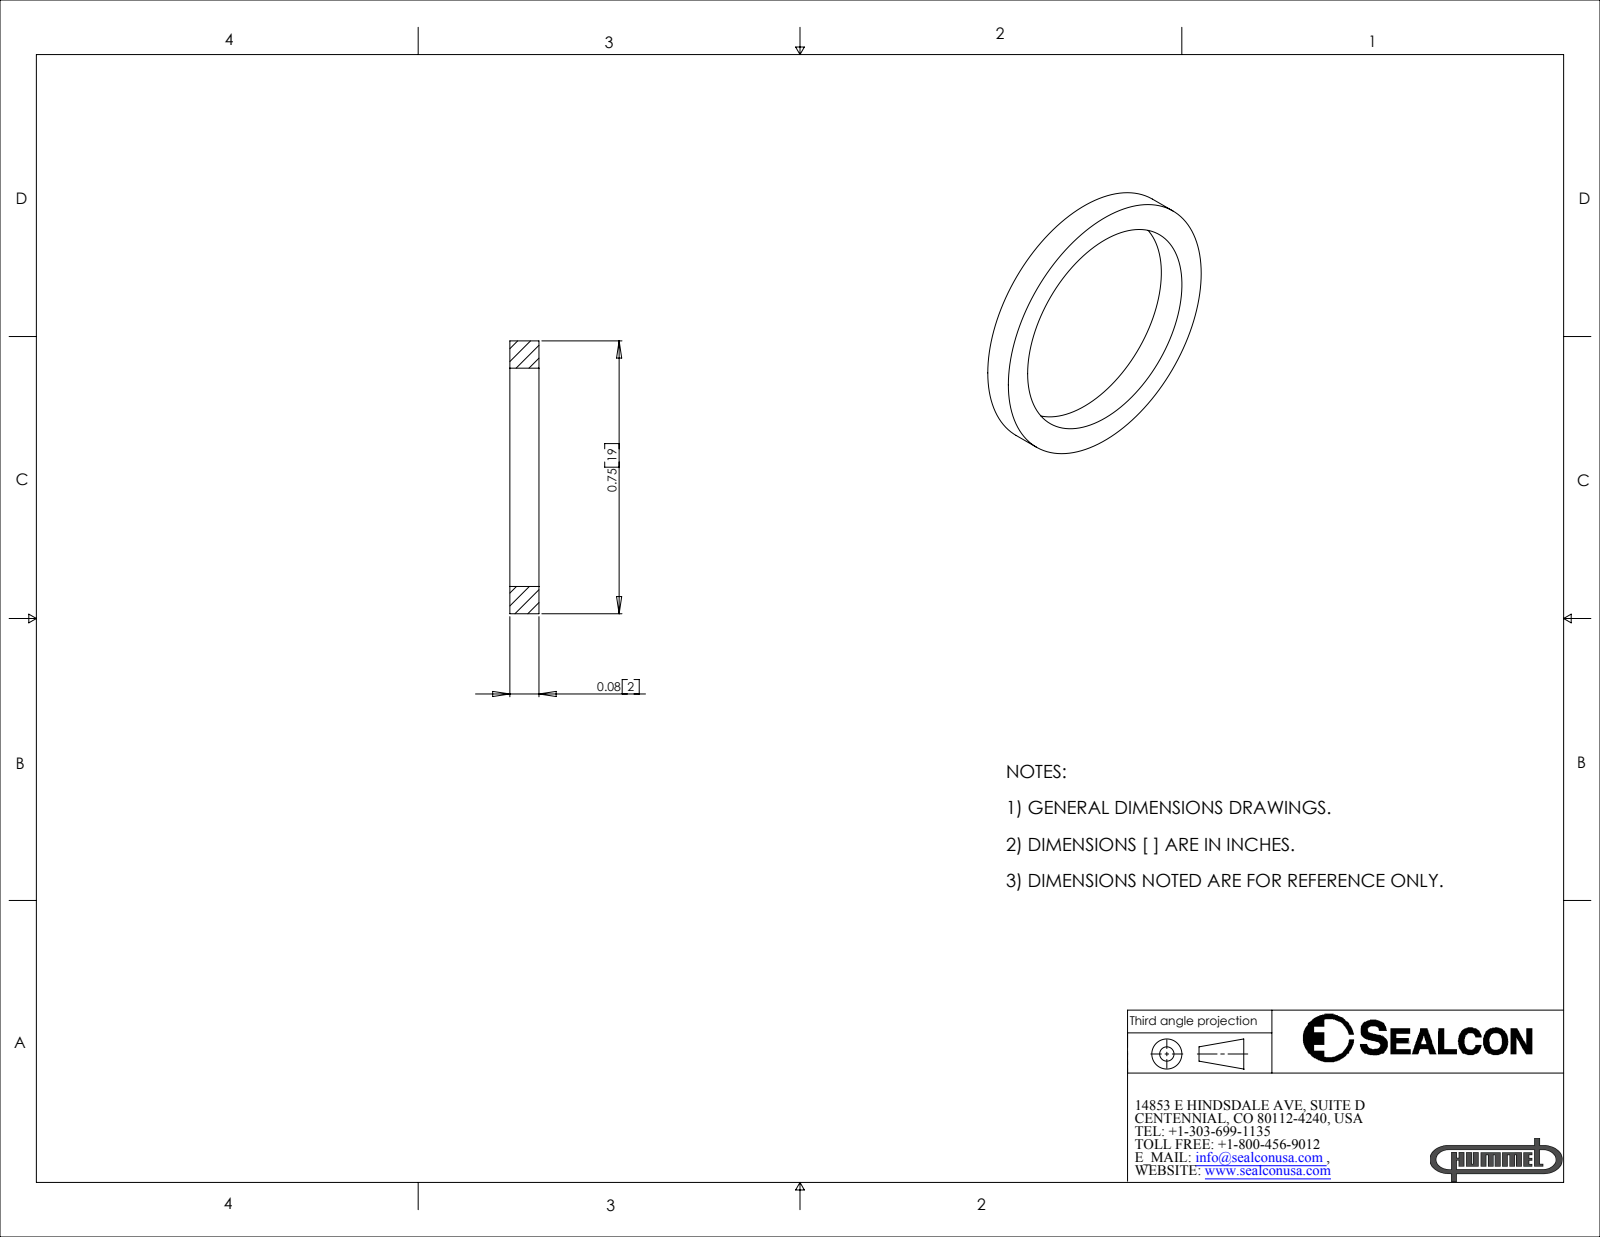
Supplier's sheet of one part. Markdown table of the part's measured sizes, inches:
| quantity | value |
| --- | --- |
| part name | SR-09-VT |
| STEP written by | SolidWorks 2007 (CONFIG_CONTROL_DESIGN) |
| units | inches |
| bodies | 1 solid, 6 faces (2 planar, 4 cylindrical, 0 other) |
| overall size | 0.75 × 0.75 × 0.08 |
| volume | 0.013 in³ |
| surface area | 0.657 in² |
| round holes (diameter × count) | 0.6 × 1 |
| round bosses / shafts (diameter × count) | 0.75 × 1 |
| main face-to-face distances | 0.08 |
